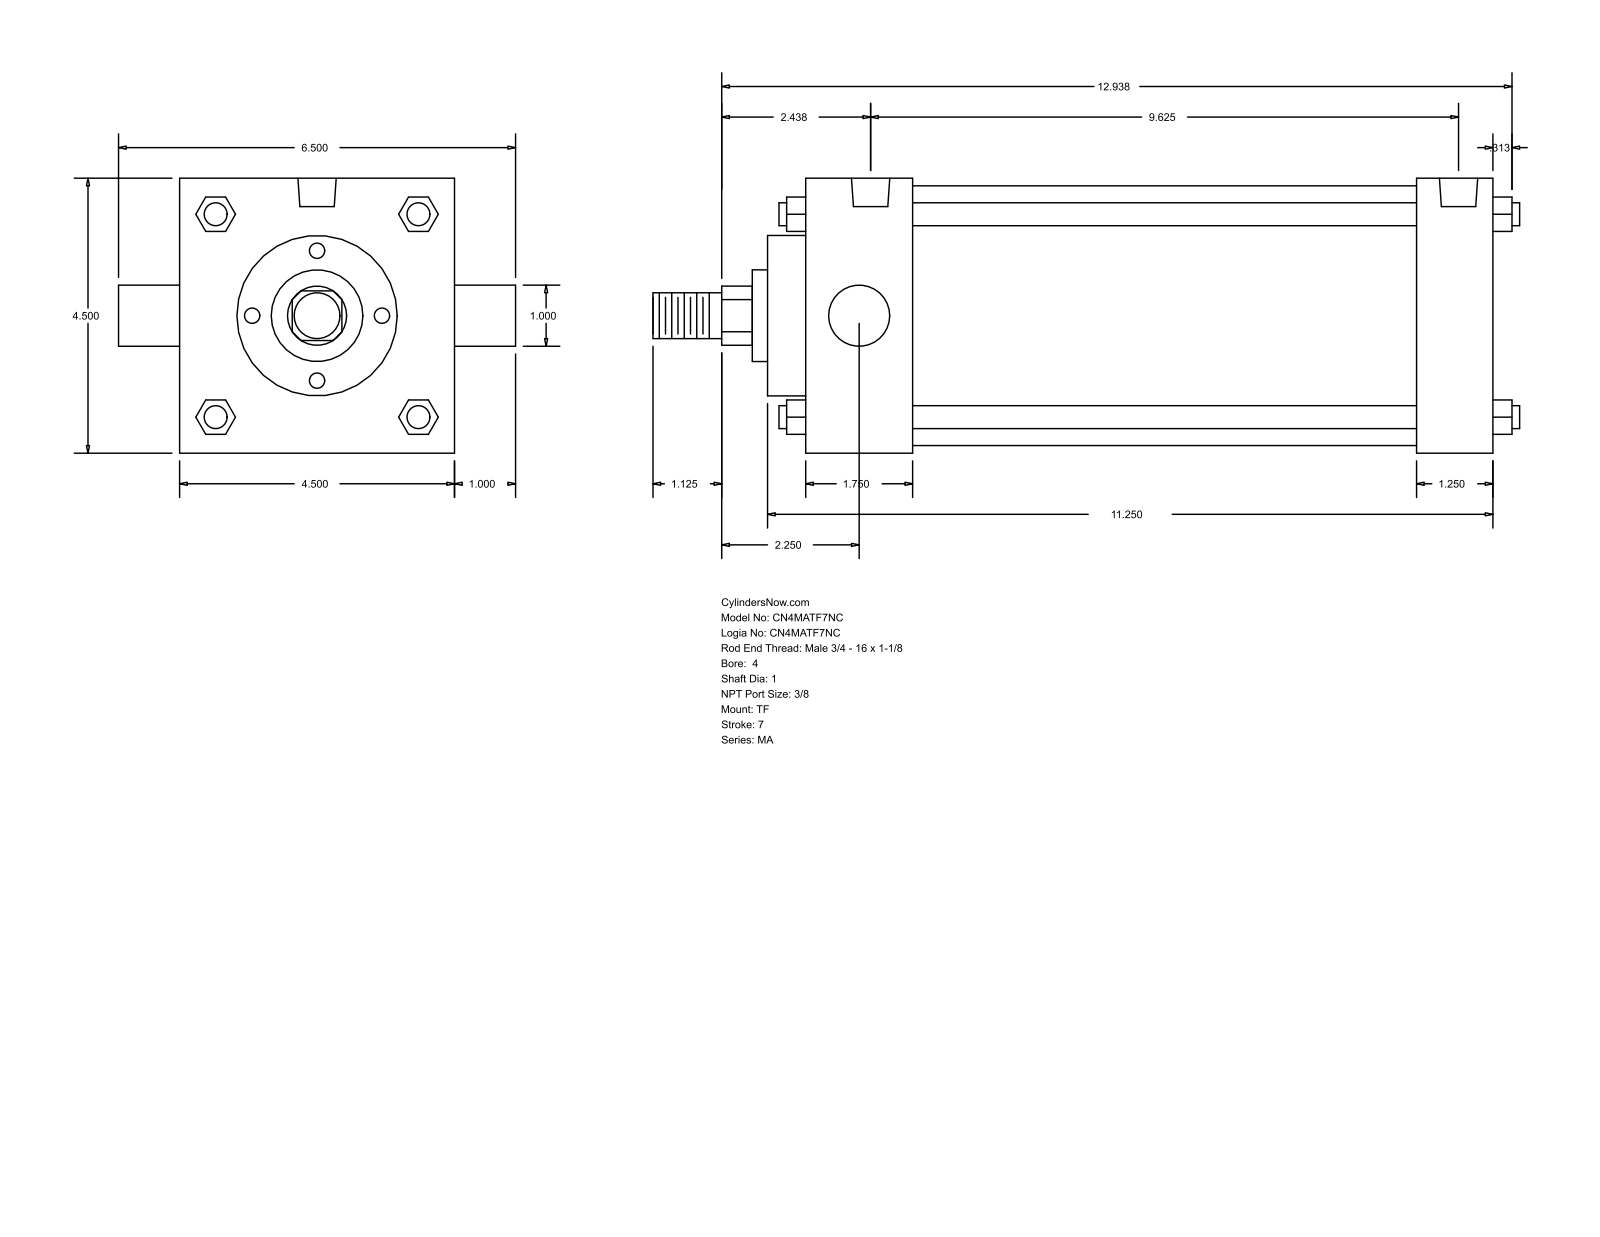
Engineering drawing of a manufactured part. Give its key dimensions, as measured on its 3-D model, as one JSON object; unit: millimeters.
{"part_name": "MA_TF__0400_1", "step_written_by": "GSSL Pune (CONFIG_CONTROL_DESIGN)", "units": "millimeters", "bodies": {"solids": 0, "faces": 122, "planar": 93, "cylindrical": 29, "other": 0}, "overall_size": [360.36, 165.1, 114.3], "round_holes": [[11.11, 3], [15.93, 2]], "round_bosses_or_shafts": [[9.53, 4], [25.4, 2], [107.95, 1], [66.67, 1], [38.1, 1], [19.05, 1]], "partial_cylinders_radius": [[12.29, 1]], "face_to_face_distances": [114.3, 285.76, 254.01, 31.75, 44.46, 209.55, 241.3, 15.87, 60.33, 269.88], "hole_center_spacings": [4.76, 4.77, 234.95, 239.71, 239.72, 244.48]}
